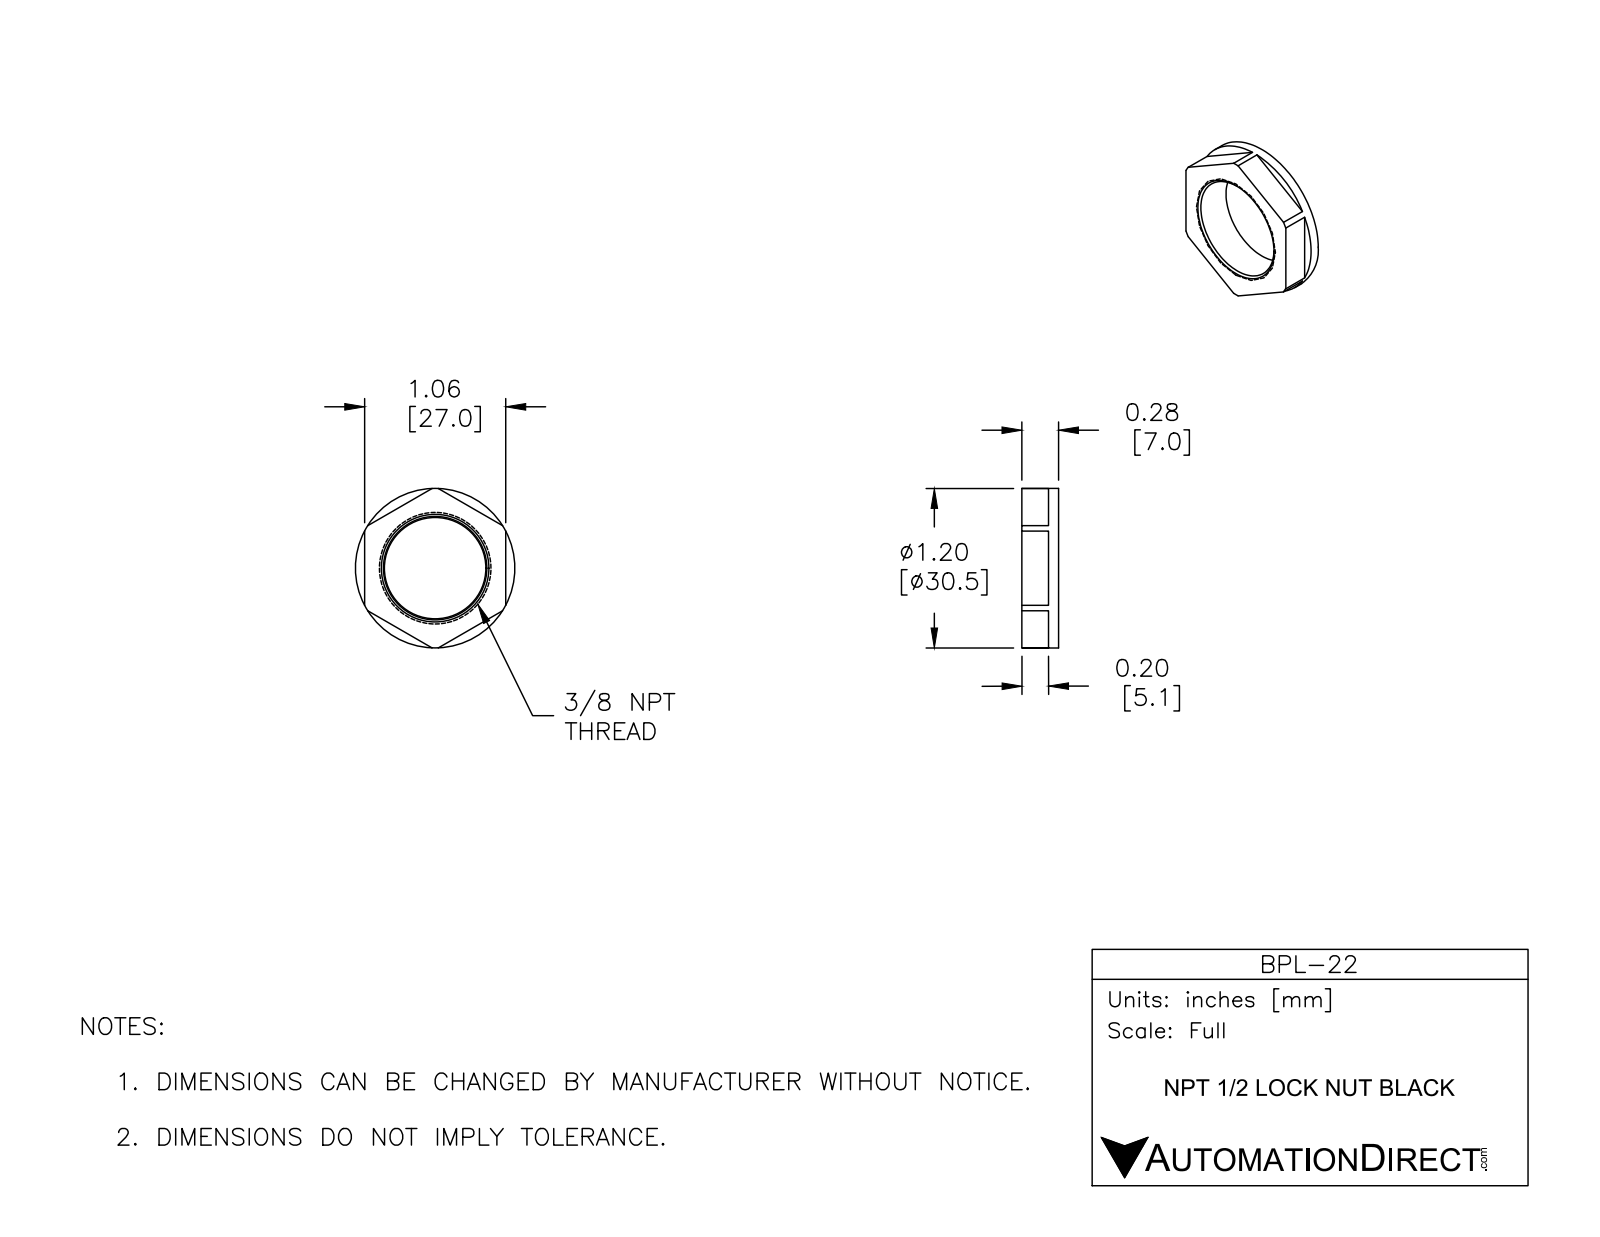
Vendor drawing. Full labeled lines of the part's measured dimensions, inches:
Part name (STEP PRODUCT): BPL-22
STEP written by: SolidWorks 2015 (CONFIG_CONTROL_DESIGN)
Units: inches
Bodies: 1 solid, 20 faces (14 planar, 2 cylindrical, 4 other)
Overall size (bounding box): 1.2 × 1.2 × 0.276
Volume: 0.13 in³ · Surface area: 2.872 in²
Round bosses / shafts (diameter × count): ⌀1.2 ×1
Main face-to-face distances: 0.276, 1.062, 0.076, 0.2
